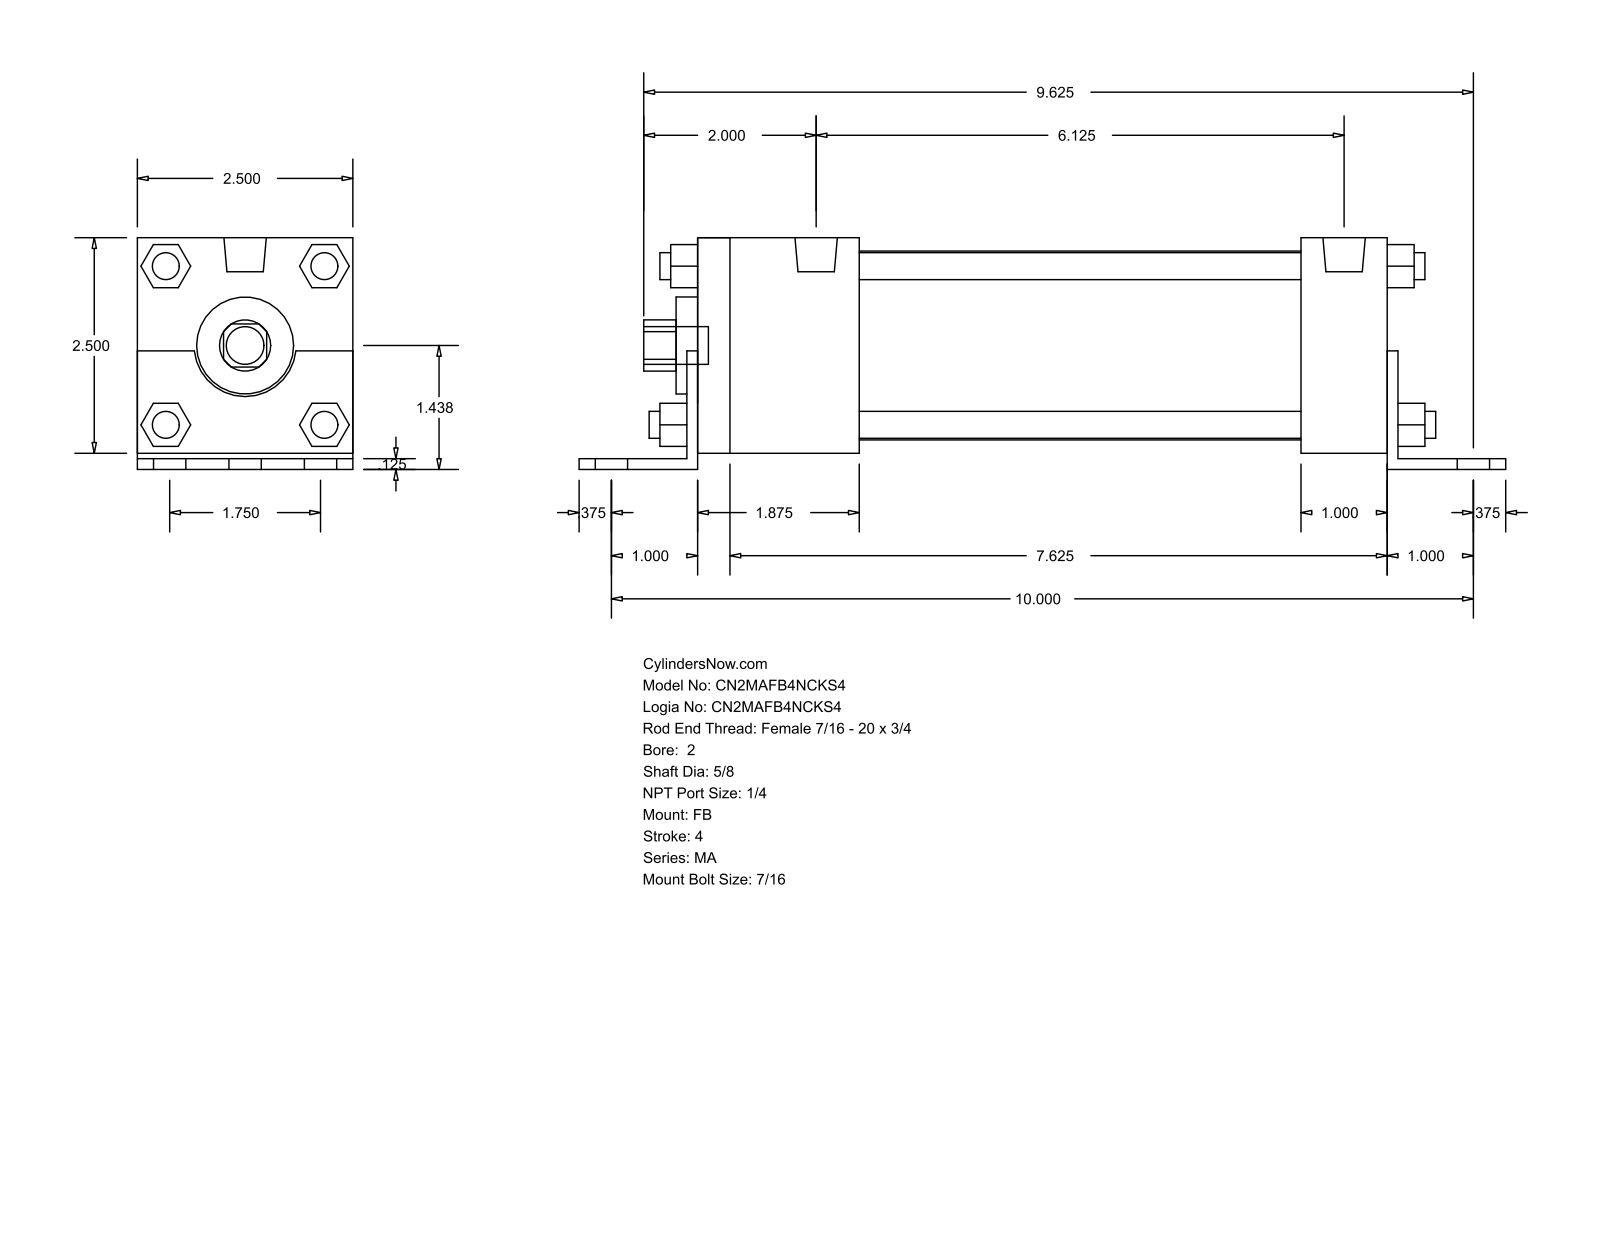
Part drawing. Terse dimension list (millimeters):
name: MA_FB__0200_0.625
written by: GSSL Pune (CONFIG_CONTROL_DESIGN)
unit: mm
bodies: 0 solids, 140 faces (105 planar, 35 cylindrical, 0 other)
size: 273.05 × 68.26 × 63.5
holes: 1× ⌀15.88, 1× ⌀28.57, 1× ⌀55.63
bosses: 8× ⌀7.94, 7× ⌀11.11, 2× ⌀12.49
rounds: 1× R7.54, 1× R15.05
face distances: 63.5, 4.76, 3.17, 68.26, 1.59, 3.18, 65.09, 206.37, 203.19, 12.7
